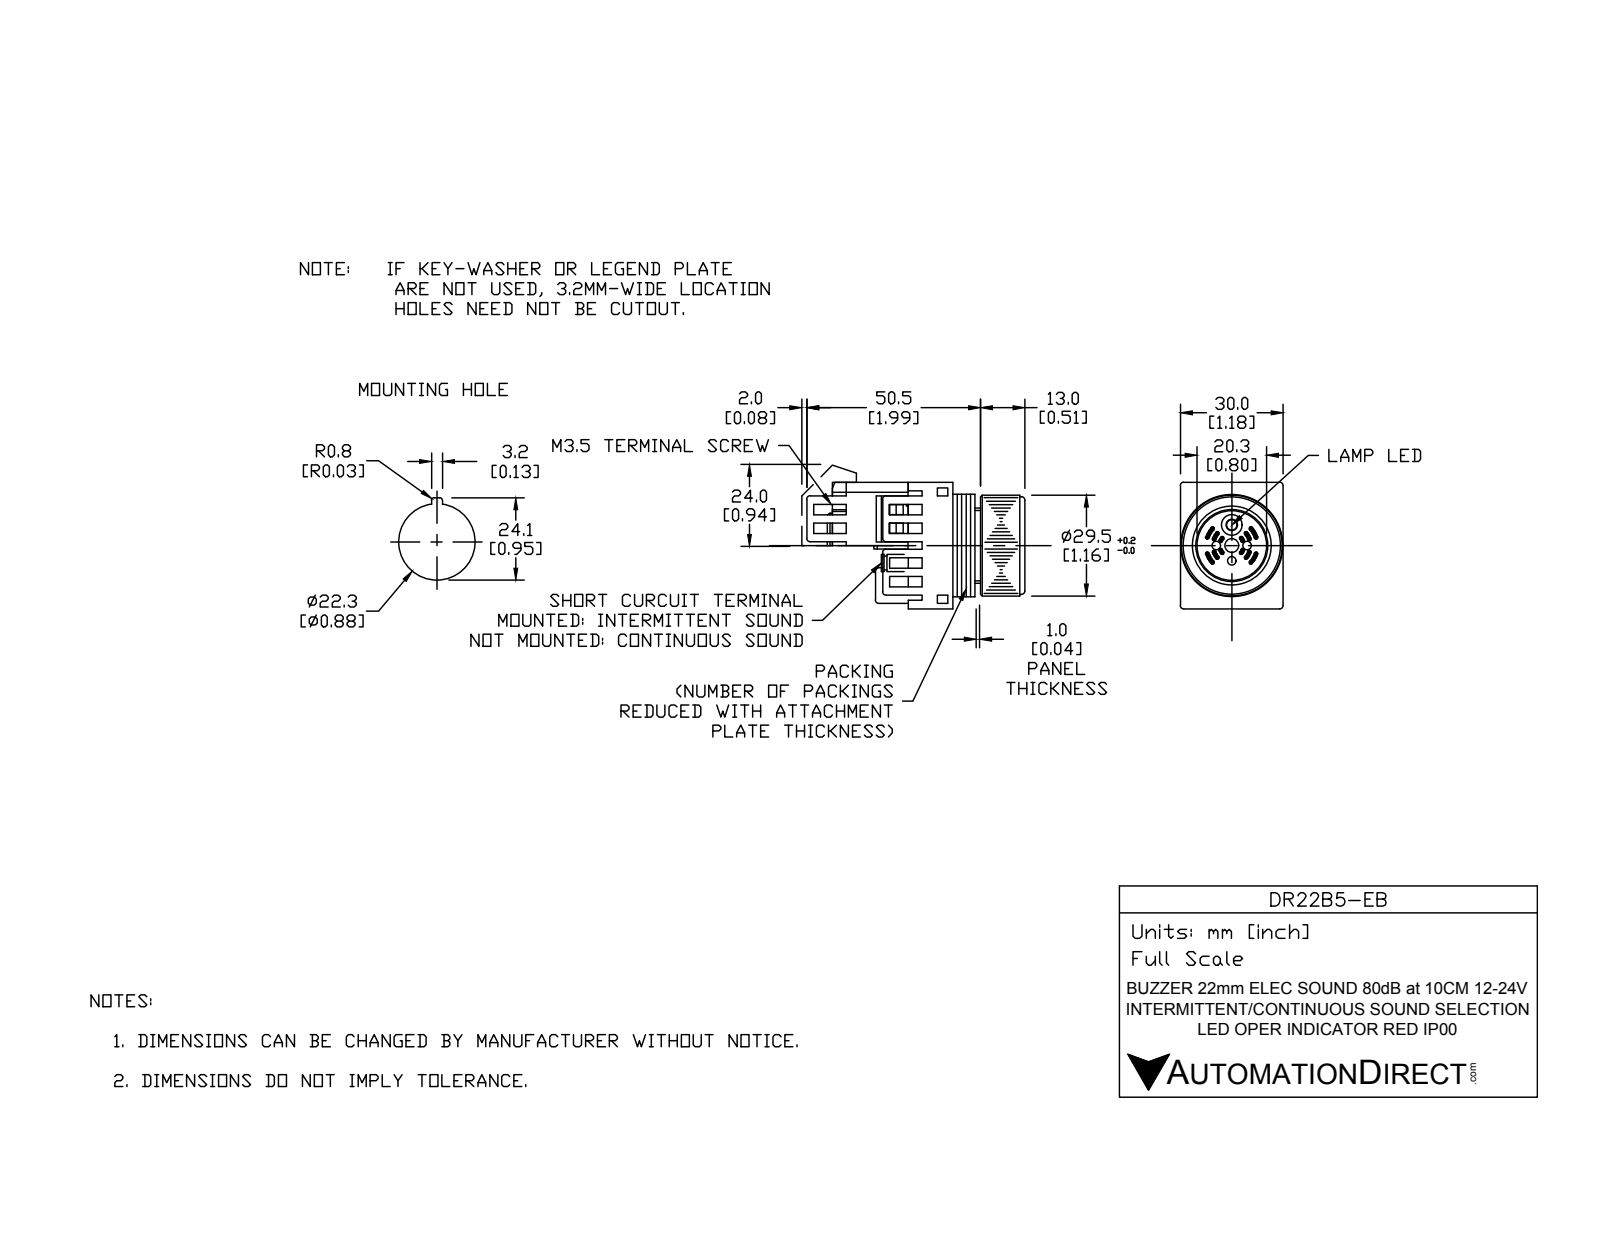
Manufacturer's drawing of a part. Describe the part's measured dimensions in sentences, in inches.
The part is named "DR22B5-EB". Its 3-D file was written by "SolidWorks 2017 (AUTOMOTIVE_DESIGN)". It is 13 solids with 196 faces: 113 planar, 71 cylindrical and 12 other. Overall it measures 2.5 by 1.654 by 1.213 inches. Its volume is 2.421 cubic inches and its surface area 30.91 square inches. Round holes: 3 of diameter 0.087, 2 of diameter 0.276, 1 of diameter 0.098, 1 of diameter 0.157, 1 of diameter 0.819, 1 of diameter 0.886. Round bosses or shafts: 2 of diameter 0.197, 1 of diameter 1.213, 1 of diameter 1.161, 1 of diameter 0.866, 1 of diameter 0.795. Partial cylindrical surfaces (rounded edges, fillets, slot ends): 10 of radius 0.02, 2 of radius 0.079, 2 of radius 0.177. The main face-to-face distances are 0.059, 0.118, 0.049, 0.177, 0.108, 0.069, 1.181, 0.728, 0.512, 0.167. The hole center spacings are 0.177, 0.25, 0.28, 0.618, 0.722, 0.776, 0.863, 0.977.
